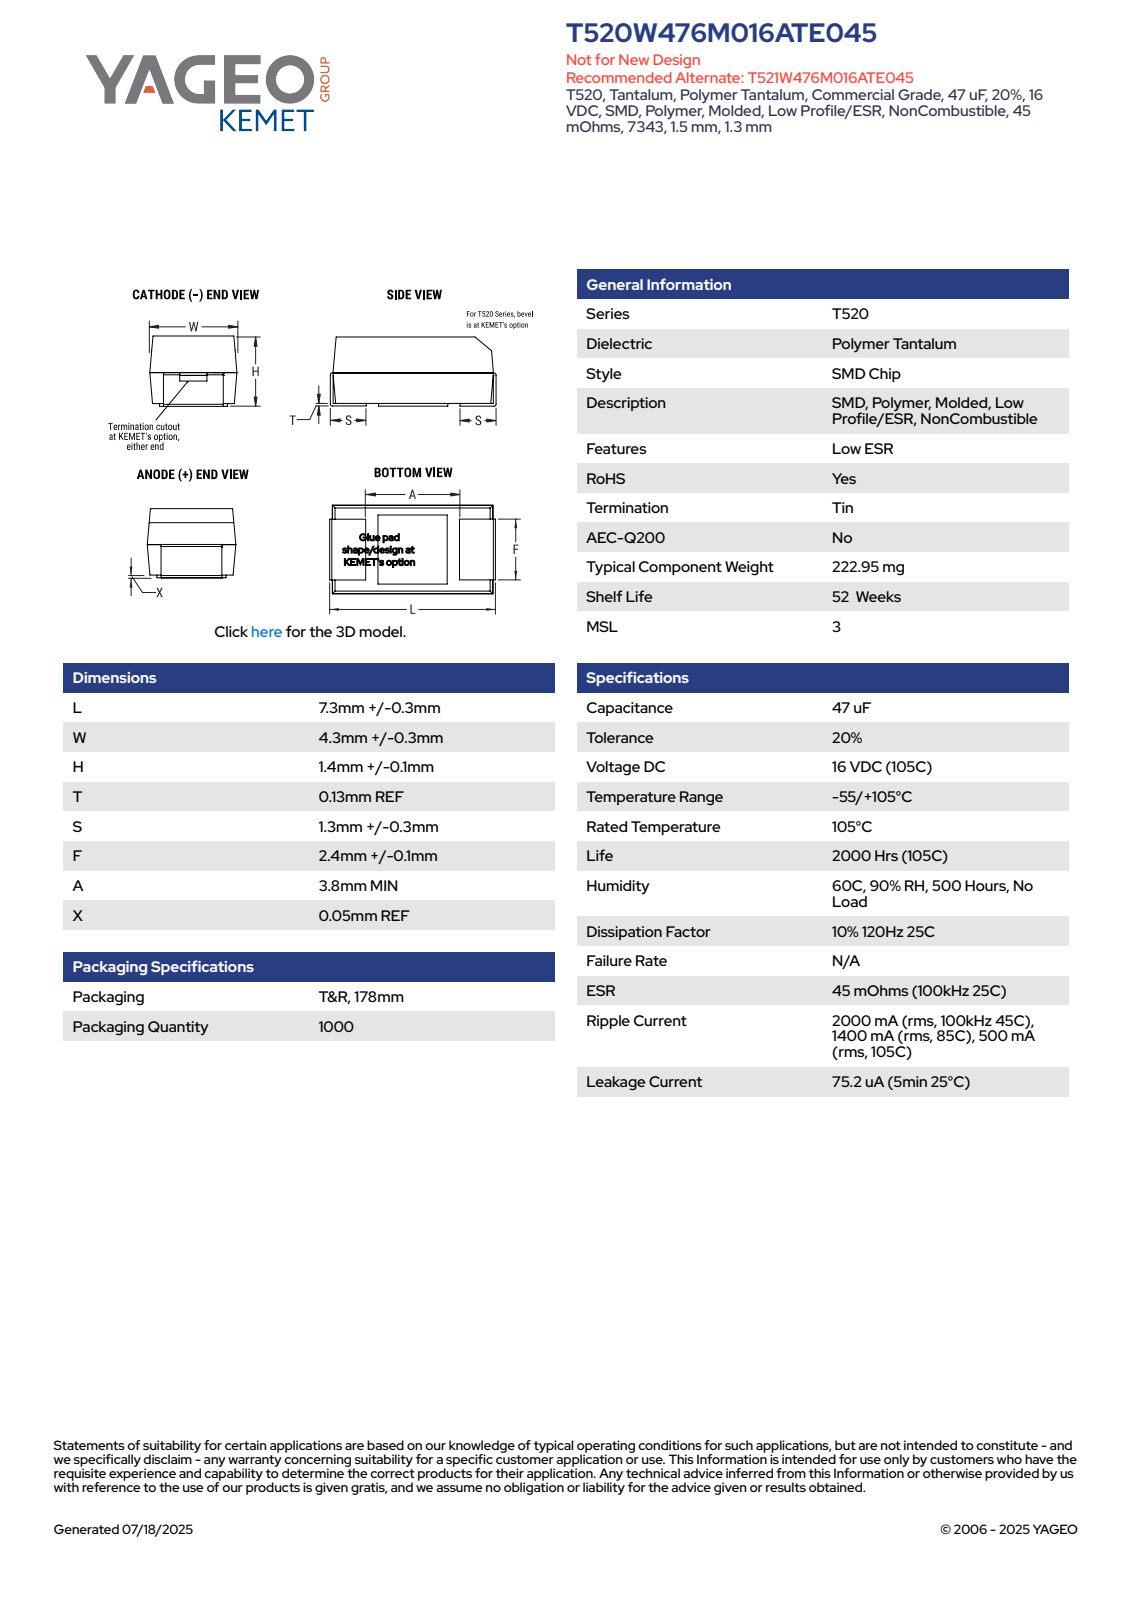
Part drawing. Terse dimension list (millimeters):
name: CTS7343W_L7.6W4.6H1.5S1.3F2.4; Case_Anode_20; Case_Top_20; Case_Cathode_20 (+1 more)
written by: SolidWorks 2014 (AUTOMOTIVE_DESIGN)
unit: mm
bodies: 7 solids, 94 faces (90 planar, 4 cylindrical, 0 other)
size: 7.6 × 4.6 × 1.5
volume: 48 mm³; area: 189 mm²
face distances: 0.77, 0.6, 1.37, 0.7, 1.47, 4.58, 0.73, 1.5, 7.31, 7.47
